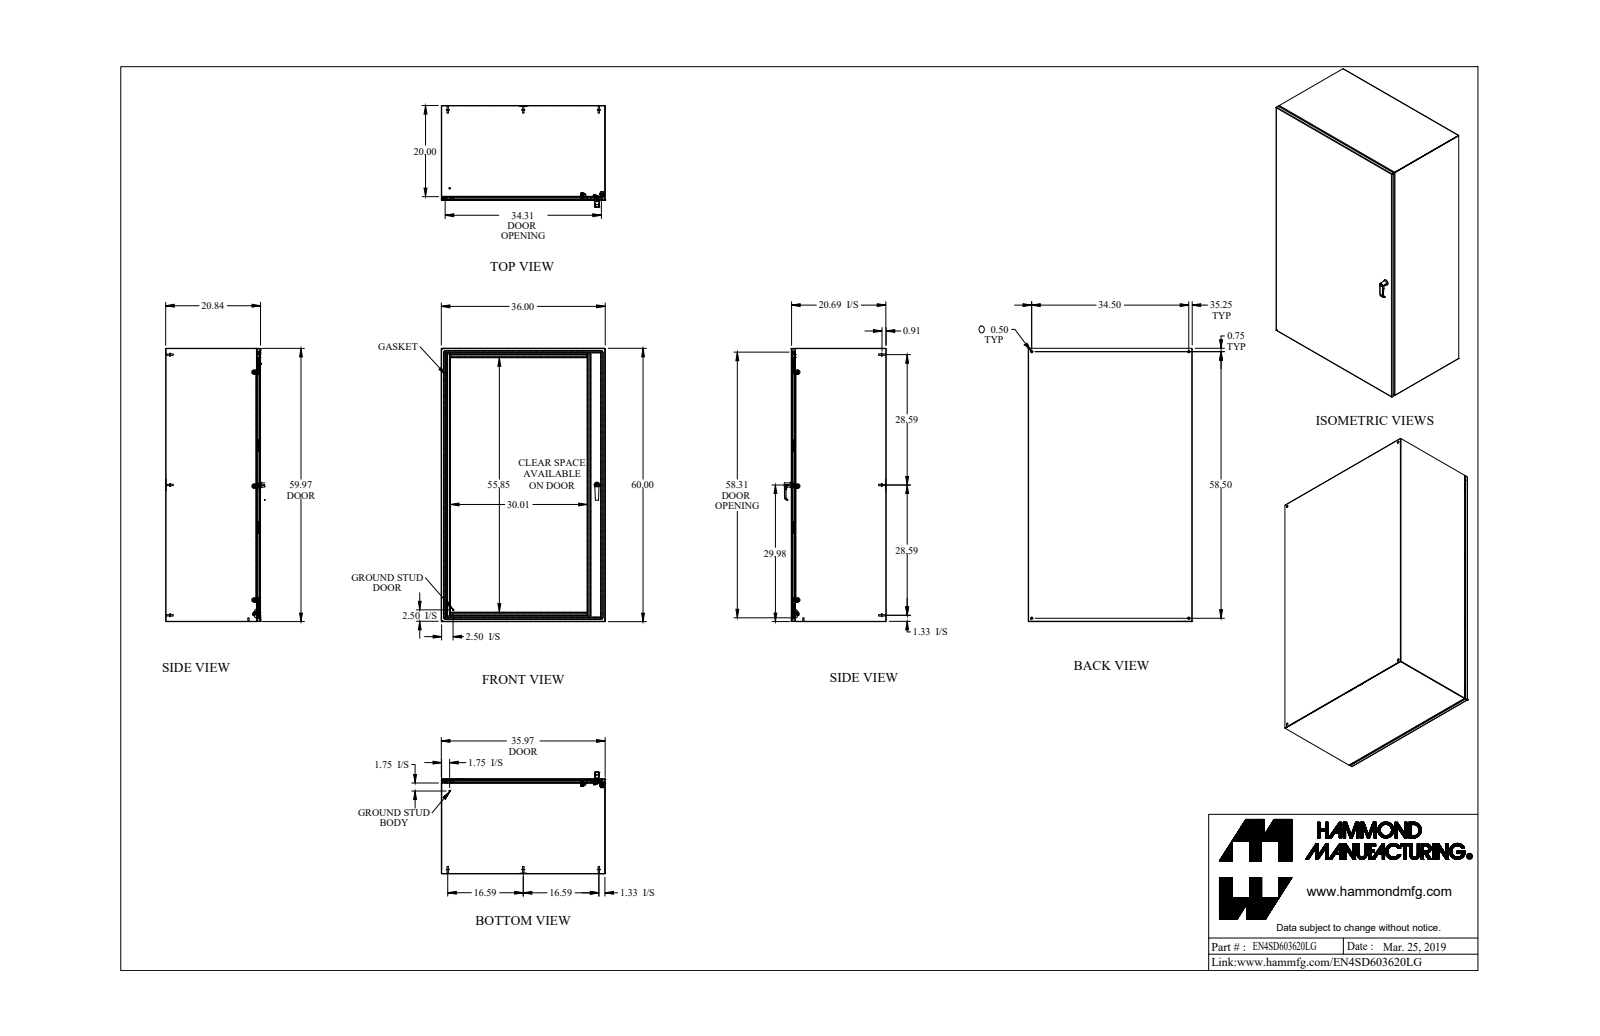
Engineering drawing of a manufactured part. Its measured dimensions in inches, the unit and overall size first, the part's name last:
Units: inches
Overall size (bounding box): 60 × 36 × 22.367
Round holes (diameter × count): ⌀0.176 ×6, ⌀0.196 ×4, ⌀0.5 ×4, ⌀0.25 ×3, ⌀0.265 ×3, ⌀0.413 ×3, ⌀0.256 ×2, ⌀0.313 ×2, ⌀0.394 ×2, ⌀0.172 ×1, ⌀0.24 ×1, ⌀0.242 ×1
Round bosses / shafts (diameter × count): ⌀0.313 ×8, ⌀0.27 ×8, ⌀0.25 ×7, ⌀0.625 ×6, ⌀0.375 ×6, ⌀0.156 ×6, ⌀1 ×3, ⌀0.625 ×3
Partial cylindrical surfaces — rounded edges, fillets, slot ends (radius × count): R0.043 ×24, R0.062 ×21, R0.036 ×17, R0.108 ×17, R0.03 ×15, R0.094 ×10, R0.016 ×9, R0.006 ×8
Main face-to-face distances: 0.072, 20.765, 35.928, 20.693, 20.837, 59.928, 35.856, 36, 59.856, 60
Hole centre spacings: 25, 4.398, 33.698, 34.5, 50, 54.245, 58.5, 63.709
Volume: 662.4 in³ · Surface area: 18 648 in²
Bodies: 64 solids, 1715 faces (761 planar, 632 cylindrical, 322 other)
Part name (STEP PRODUCT): EN4SD603620LG
STEP written by: SolidWorks 2018 (AUTOMOTIVE_DESIGN)
